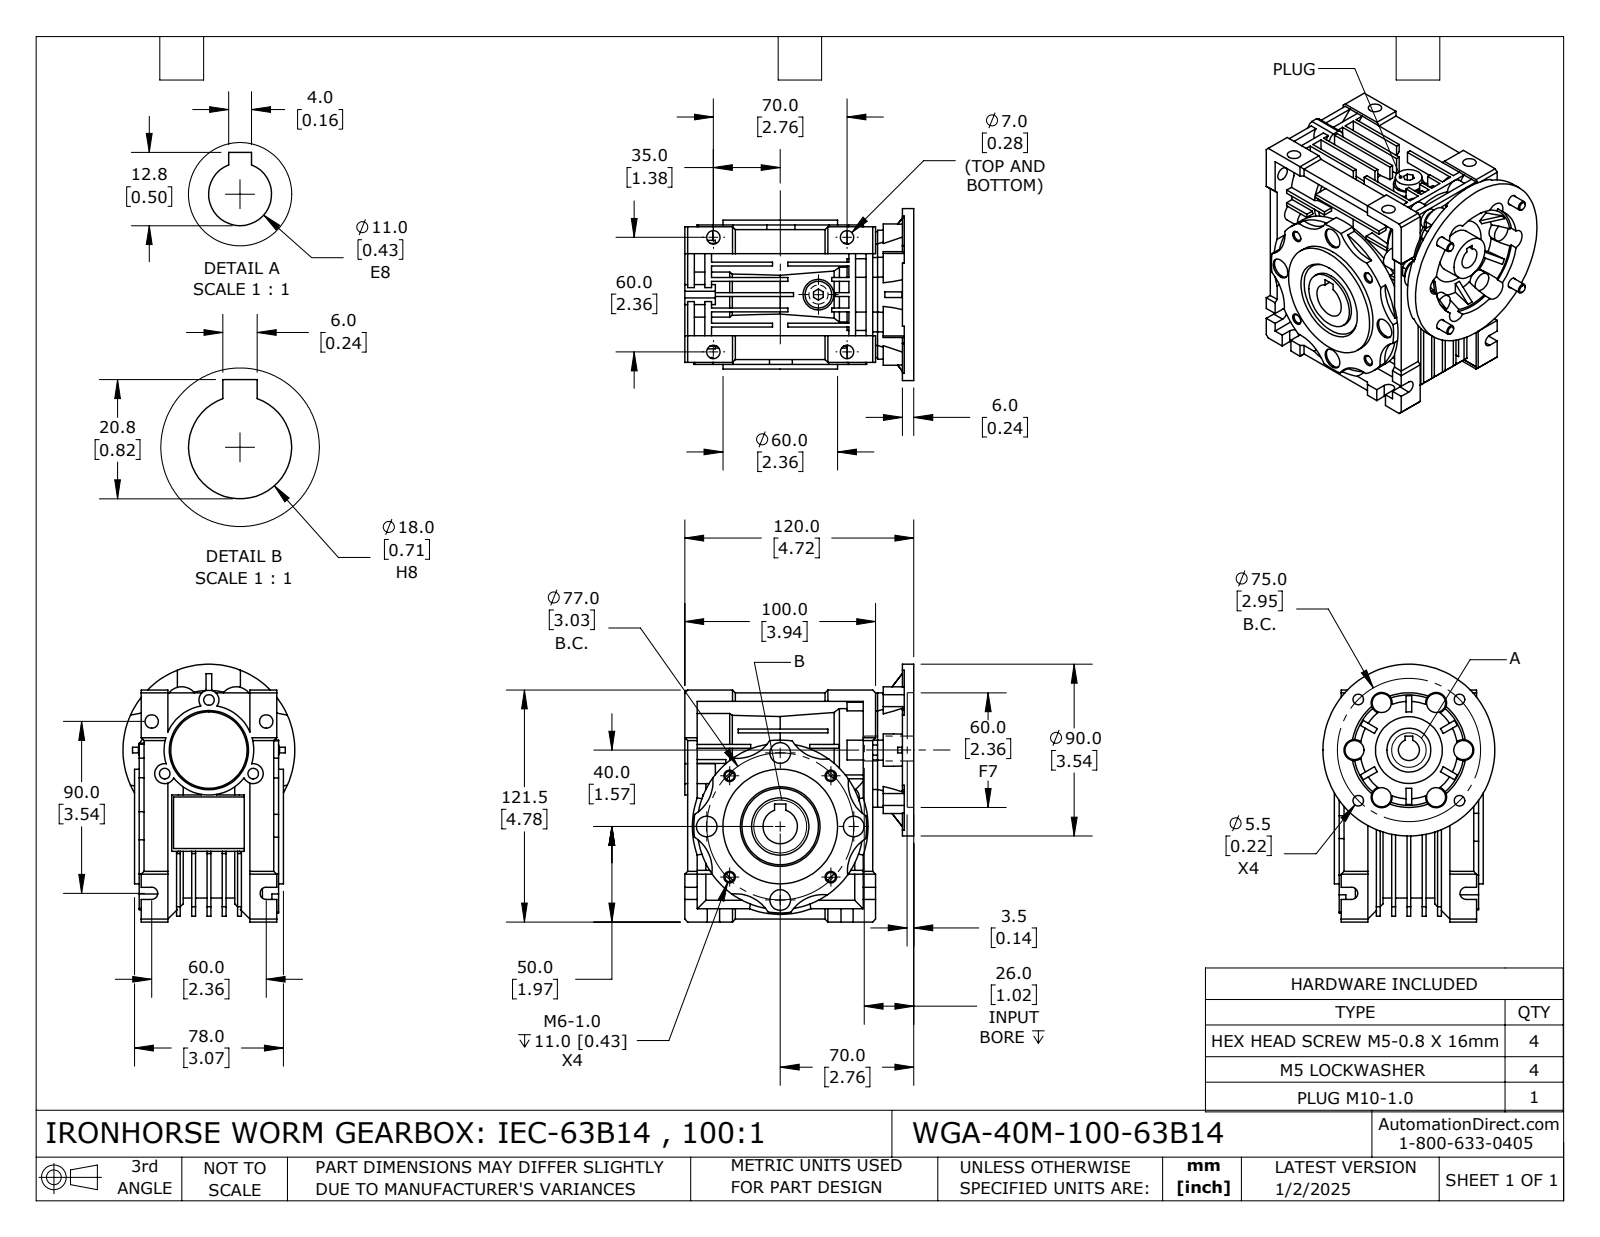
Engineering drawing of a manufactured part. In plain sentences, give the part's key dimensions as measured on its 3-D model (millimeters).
The part is named "WGA-40M-100-63B14". Its 3-D file was written by "SolidWorks 2024 (CONFIG_CONTROL_DESIGN)". It is 14 solids with 1003 faces: 564 planar, 307 cylindrical and 132 other. Overall it measures 135 by 127.7 by 90 millimeters. Its volume is 667 307 cubic millimeters and its surface area 163 100 square millimeters. Round holes: 6 of diameter 7, 4 of diameter 4.92, 4 of diameter 5.1, 4 of diameter 5.5, 4 of diameter 10.8, 3 of diameter 5.55, 1 of diameter 9, 1 of diameter 11, 1 of diameter 11.5, 1 of diameter 18, 1 of diameter 23, 1 of diameter 28. Round bosses or shafts: 6 of diameter 10, 4 of diameter 9.2, 4 of diameter 5, 1 of diameter 90, 1 of diameter 75, 1 of diameter 60, 1 of diameter 54, 1 of diameter 47. Partial cylindrical surfaces (rounded edges, fillets, slot ends): 9 of radius 5.25, 8 of radius 20, 6 of radius 3.2, 6 of radius 5.22, 6 of radius 5.5, 6 of radius 8.5, 4 of radius 5.51, 1 of radius 30. The main face-to-face distances are 8, 6, 2, 1.5, 16, 10, 5, 14, 2.5, 19. The hole center spacings are 29.1, 37.5, 53.04, 70.22, 33.54, 38.5, 54.45, 75.01.
